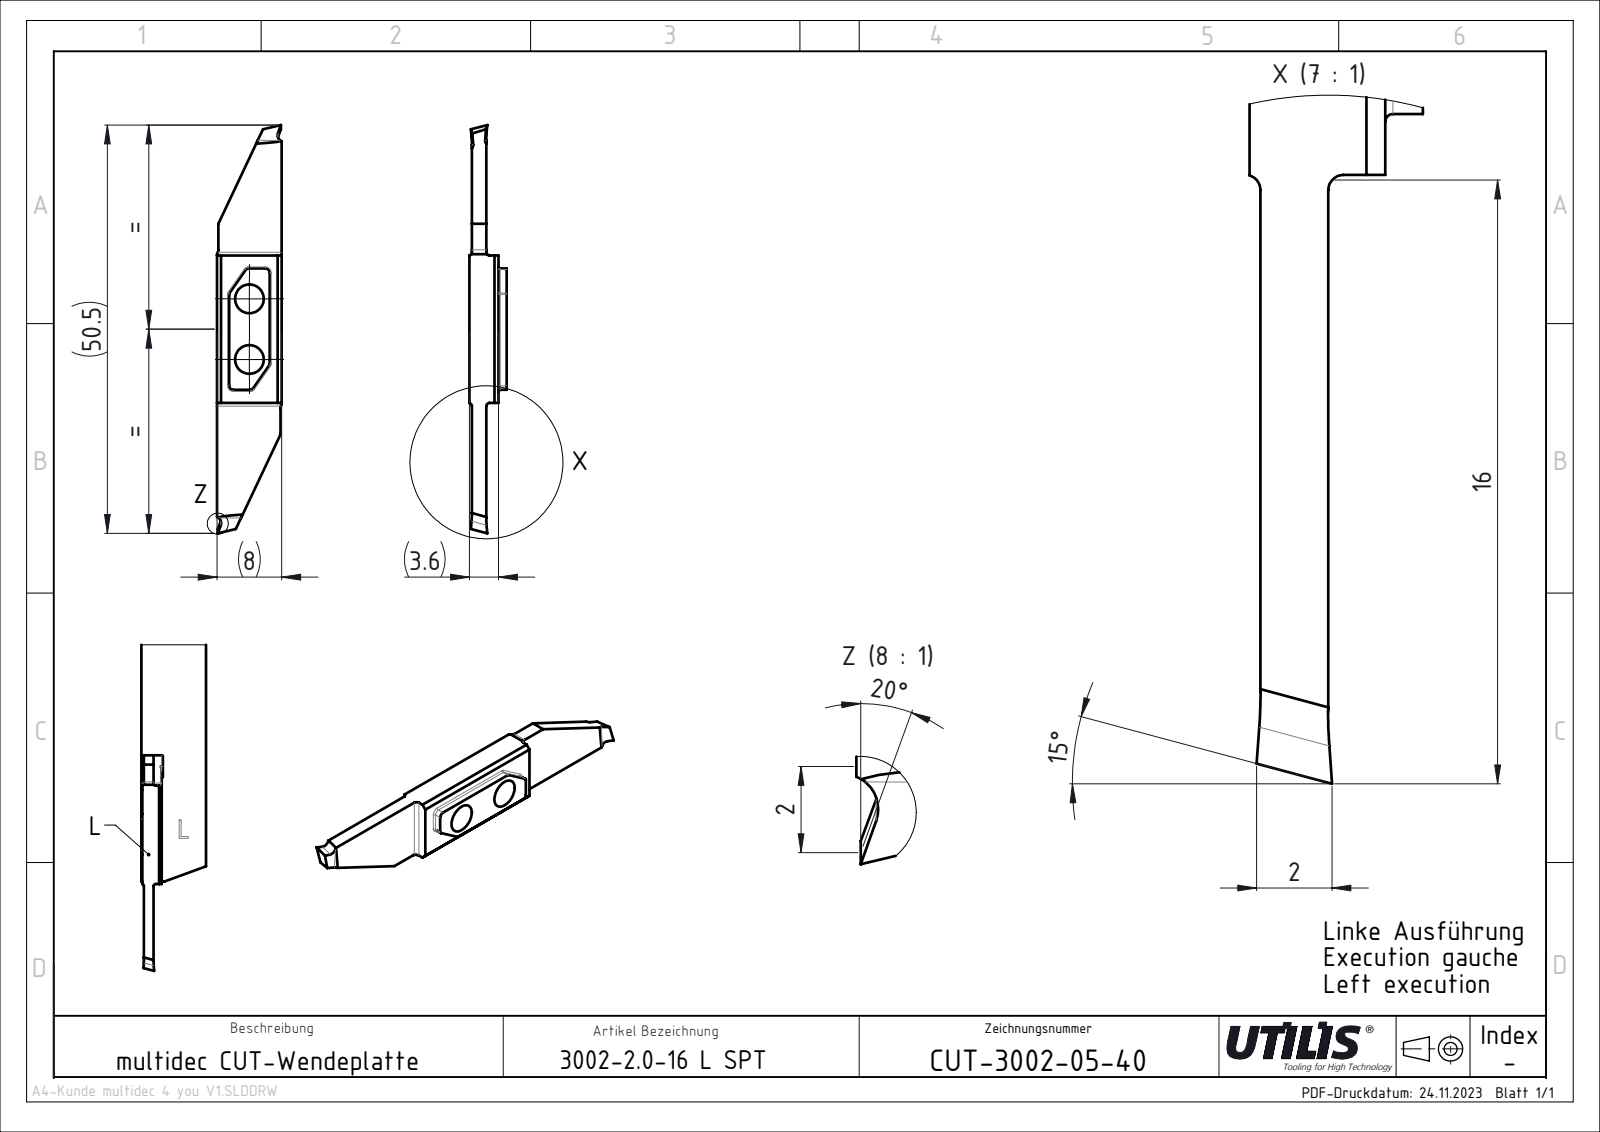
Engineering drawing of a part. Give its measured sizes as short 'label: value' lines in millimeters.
name: CUT-3002 SPT Slim_and_Deep; ASME Y14.5
written by: SolidWorks 2023 SP4 || FormatWorks Professional (AP242_MANAGED_MODEL_BASED_3D_ENGINEERING_MIM_LF)
unit: mm
bodies: 1 solid, 32 faces (22 planar, 10 cylindrical, 0 other)
size: 50.5 × 8 × 3.6
volume: 778 mm³; area: 968 mm²
holes: 2× ⌀3.55
rounds: 4× R0.4, 2× R1
face distances: 1.8, 2.09, 3.6, 3.31, 1.51, 8, 18.09, 7.85, 0.6, 18.22
hole spacings: 7.5
